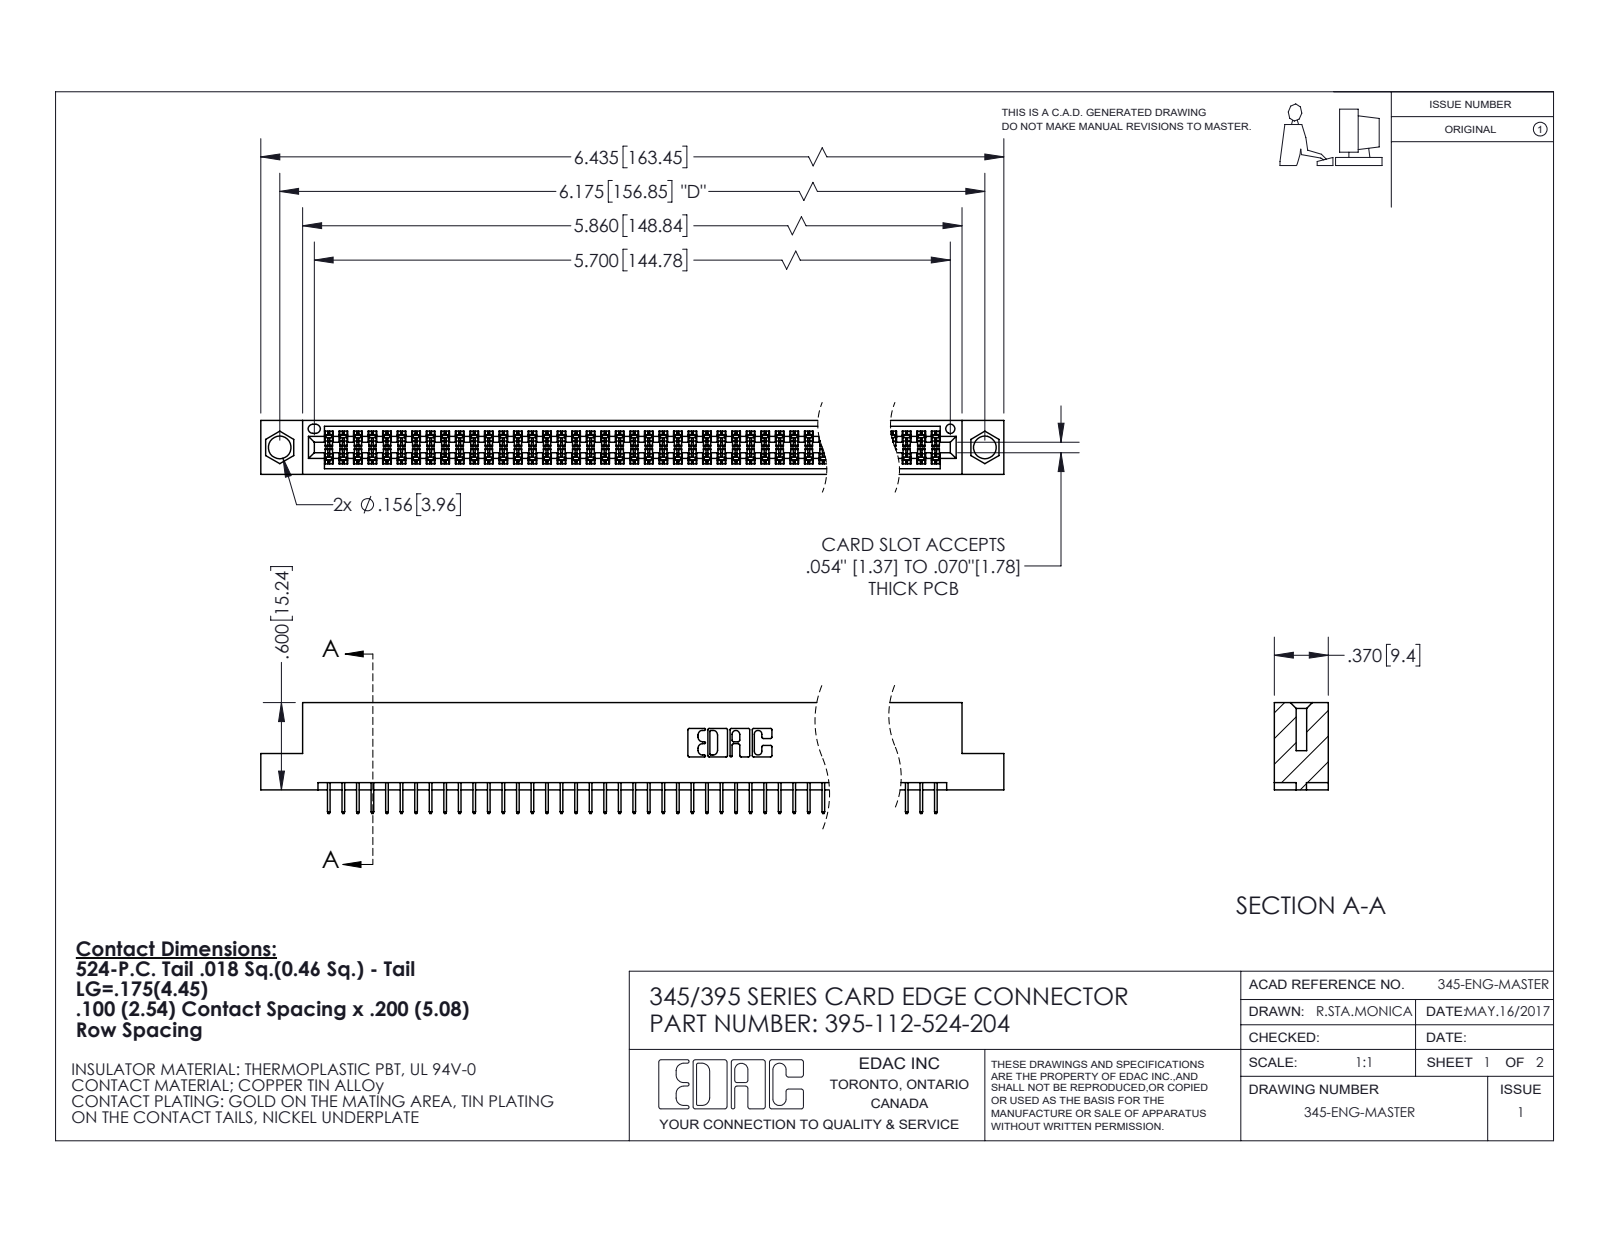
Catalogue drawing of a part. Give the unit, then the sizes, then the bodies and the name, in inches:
Units: inches
Overall size (bounding box): 6.435 × 0.762 × 0.37
Round holes (diameter × count): ⌀0.156 ×2, ⌀0.064 ×1
Partial cylindrical surfaces — rounded edges, fillets, slot ends (radius × count): R0.006 ×169, R0.01 ×22, R0.007 ×6, R0.031 ×6, R0.026 ×3, R0.014 ×2, R0.019 ×2, R0.022 ×2
Main face-to-face distances: 0.072, 0.298, 0.2, 0.37, 0.098, 0.272, 0.025, 0.225, 0.072, 0.175
Hole centre spacings: 0.27, 5.939, 6.175
Volume: 0.96 in³ · Surface area: 35.54 in²
Bodies: 113 solids, 6188 faces (4462 planar, 1726 cylindrical, 0 other)
Part name (STEP PRODUCT): 345-292-001_345-293-124; 395-112-524-204; 345 Part_Flush Mounting Lugs - 0.156 Dia-TI
STEP written by: SolidWorks 2020 (CONFIG_CONTROL_DESIGN)
